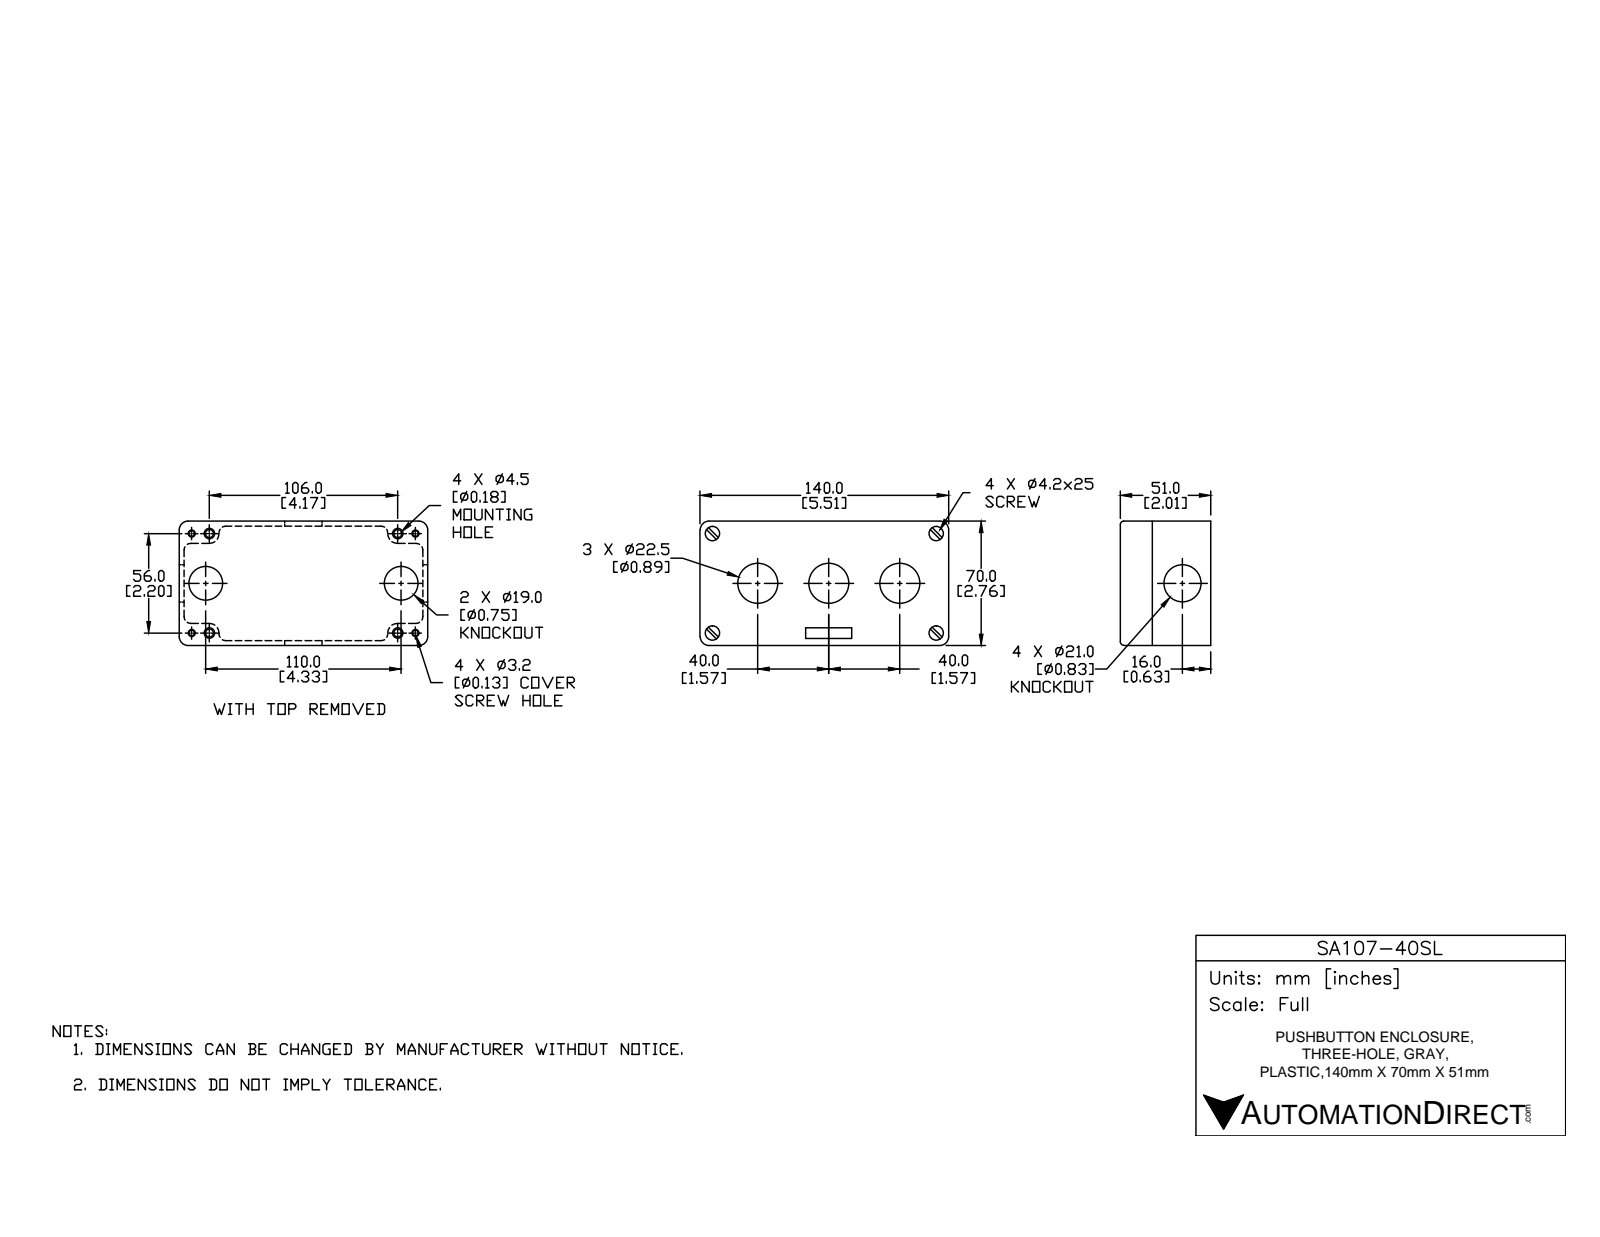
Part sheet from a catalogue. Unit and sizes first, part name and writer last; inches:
Units: inches
Overall size (bounding box): 5.512 × 2.756 × 1.965
Round holes (diameter × count): ⌀0.126 ×4, ⌀0.165 ×4, ⌀0.177 ×4, ⌀0.295 ×4, ⌀0.315 ×4, ⌀0.886 ×3, ⌀0.748 ×2, ⌀0.827 ×2
Round bosses / shafts (diameter × count): ⌀0.291 ×4, ⌀0.11 ×4
Partial cylindrical surfaces — rounded edges, fillets, slot ends (radius × count): R0.02 ×16, R0.041 ×8, R0.095 ×8, R0.039 ×4, R0.071 ×4, R0.197 ×4, R0.259 ×4, R0.323 ×4
Main face-to-face distances: 0.087, 1.959, 1.872, 0.102, 2.756, 2.654, 0.079, 1.88, 1.793, 0.215
Hole centre spacings: 0.394, 1.105, 1.146, 1.215, 1.427, 2.205, 2.24, 2.36
Volume: 8.21 in³ · Surface area: 125.8 in²
Bodies: 6 solids, 475 faces (127 planar, 194 cylindrical, 154 other)
Part name (STEP PRODUCT): SA107-40SL
STEP written by: SolidWorks 2018 (AUTOMOTIVE_DESIGN)
